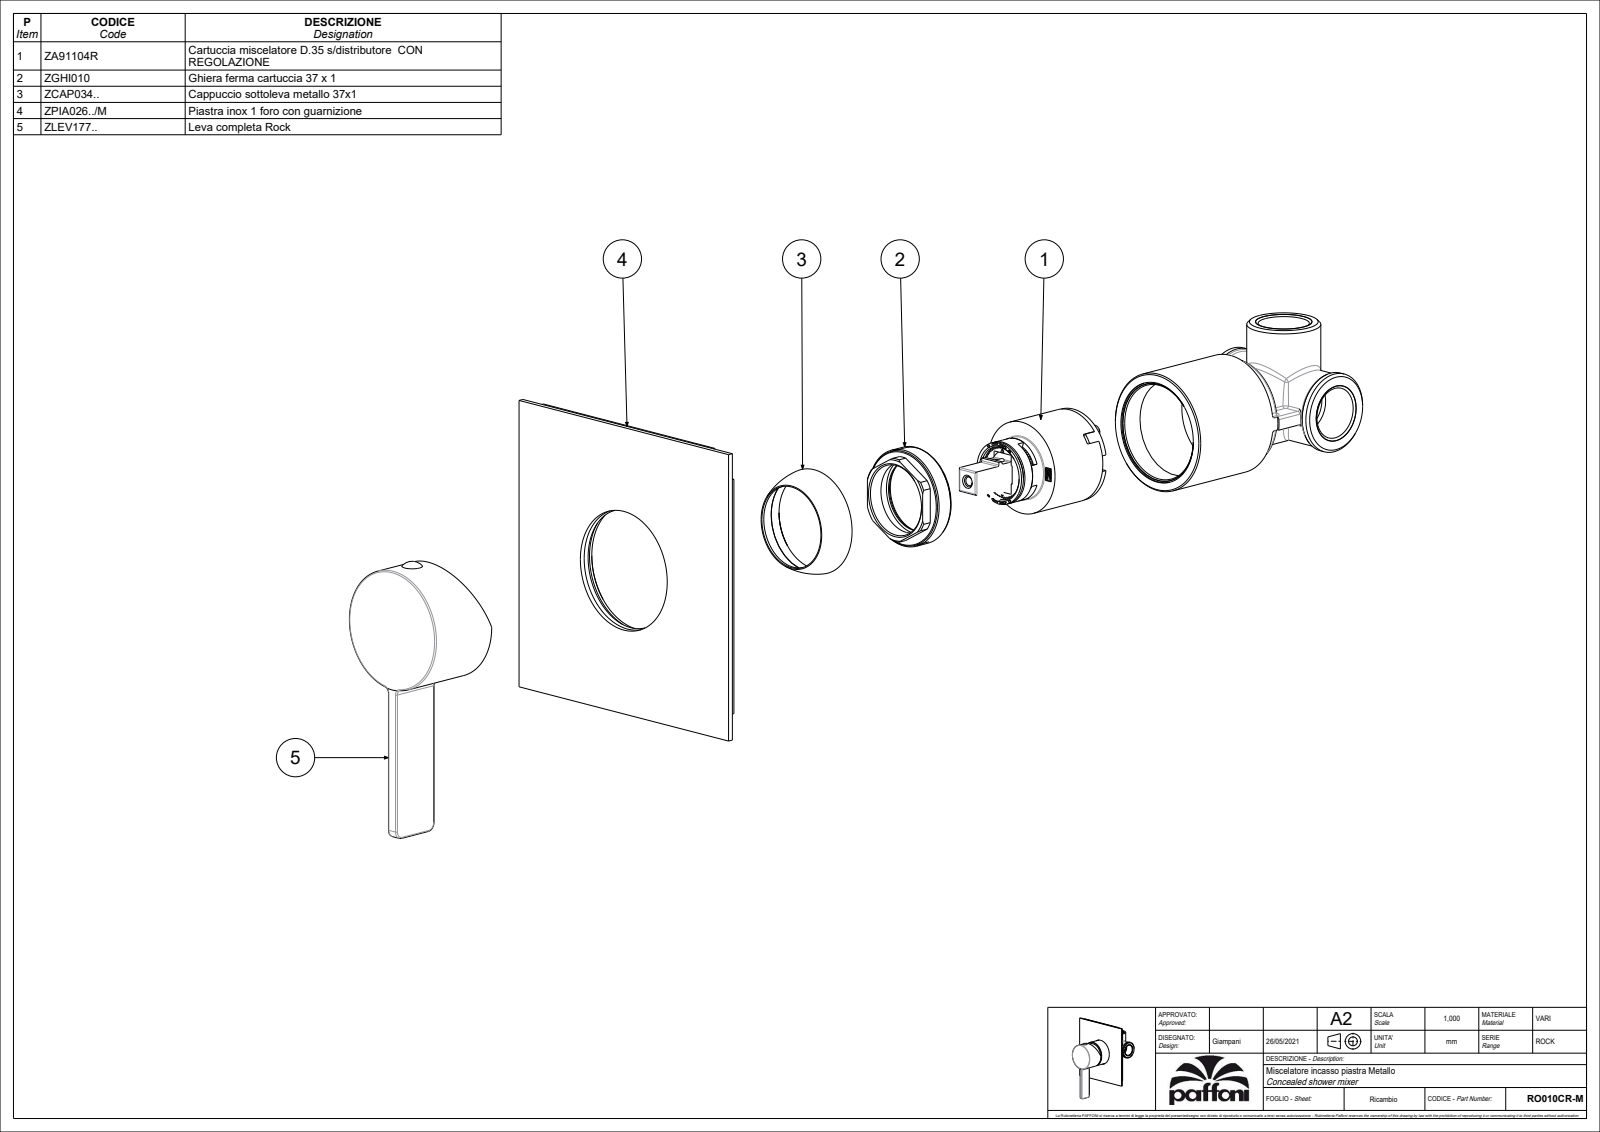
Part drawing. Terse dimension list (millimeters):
name: RO010CR-M
written by: CREO PARAMETRIC BY PTC INC, 2020044 (CONFIG_CONTROL_DESIGN)
unit: mm
bodies: 2 solids, 151 faces (50 planar, 47 cylindrical, 54 other)
size: 135 × 110 × 54.1
volume: 55 751 mm³; area: 47 042 mm²
holes: 1× ⌀3, 1× ⌀4.2, 1× ⌀5.5, 1× ⌀30.6, 1× ⌀36, 1× ⌀38
bosses: 1× ⌀45.5, 1× ⌀44.8, 1× ⌀7.6
rounds: 9× R0.5, 2× R0.3, 2× R1.5, 2× R2, 2× R3, 1× R3.5
face distances: 2, 4.5, 50.1, 48.1, 20, 52.75, 57.25, 110, 50.5, 59.5
